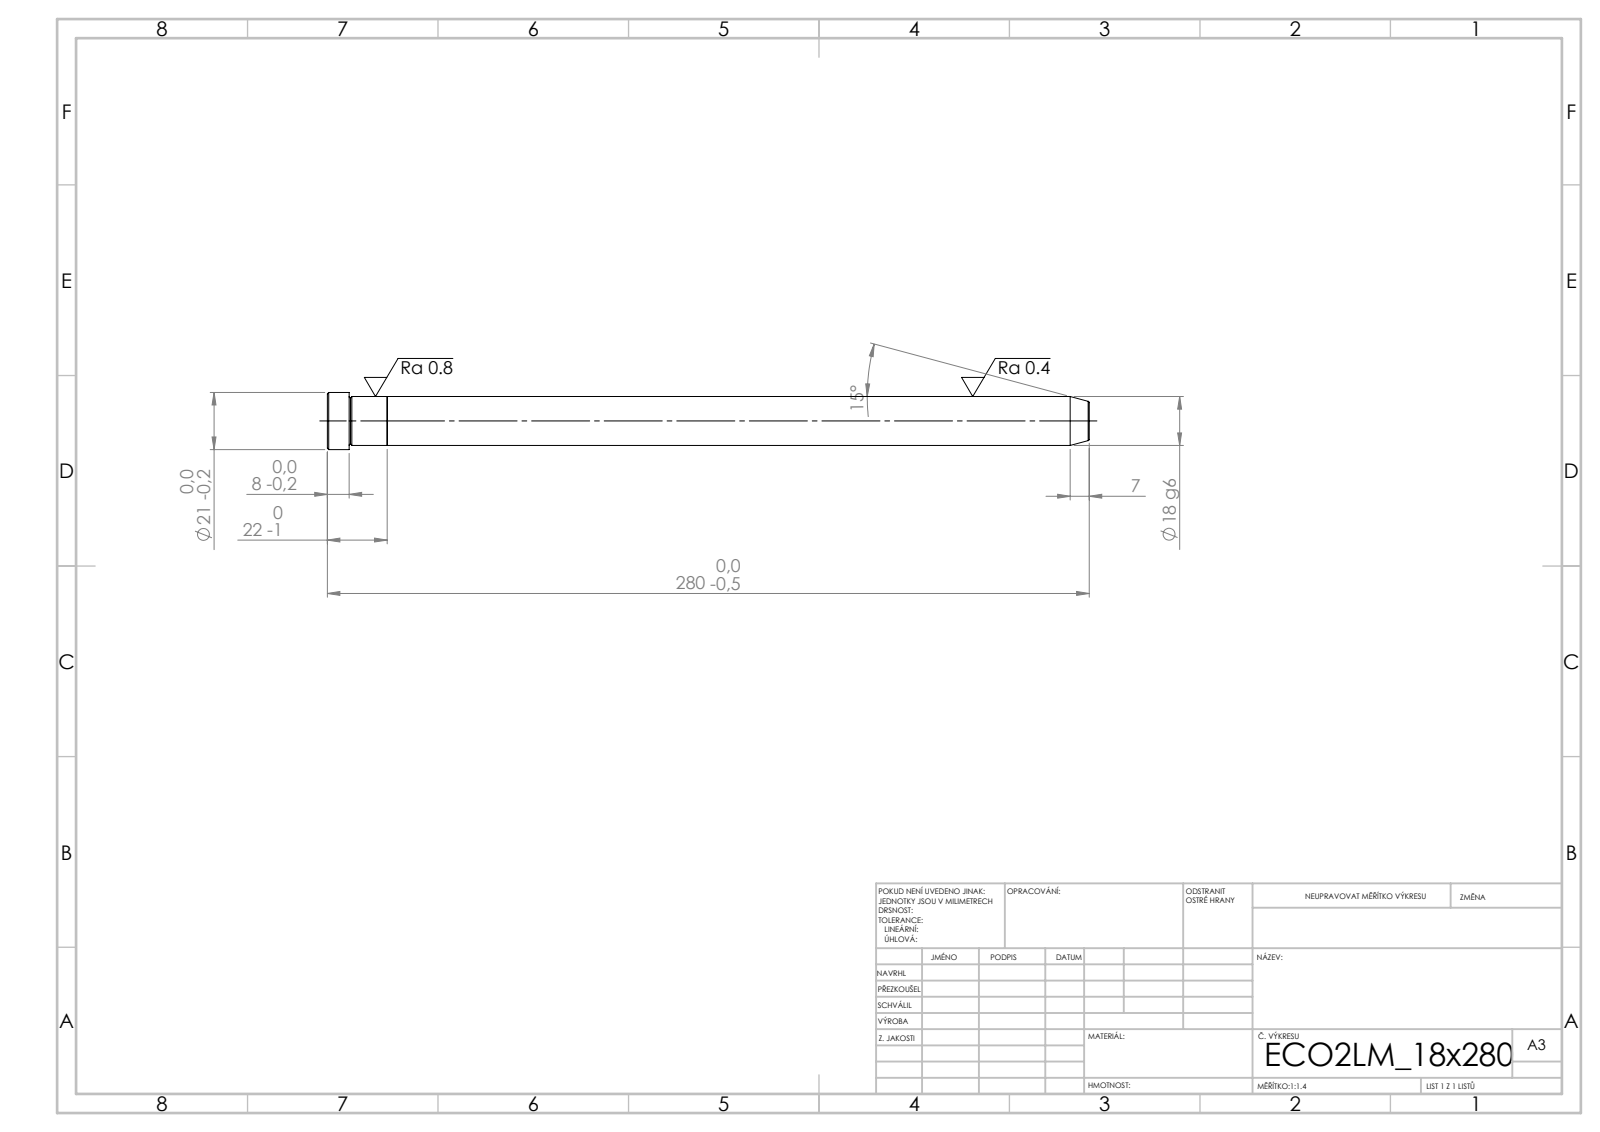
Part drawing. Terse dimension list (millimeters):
written by: SolidWorks 2019 (CONFIG_CONTROL_DESIGN)
unit: mm
bodies: 2 solids, 21 faces (5 planar, 6 cylindrical, 10 other)
size: 280 × 21 × 21
volume: 71 610 mm³; area: 16 991 mm²
bosses: 1× ⌀21, 1× ⌀18
face distances: 22, 258, 280, 272, 14, 8
